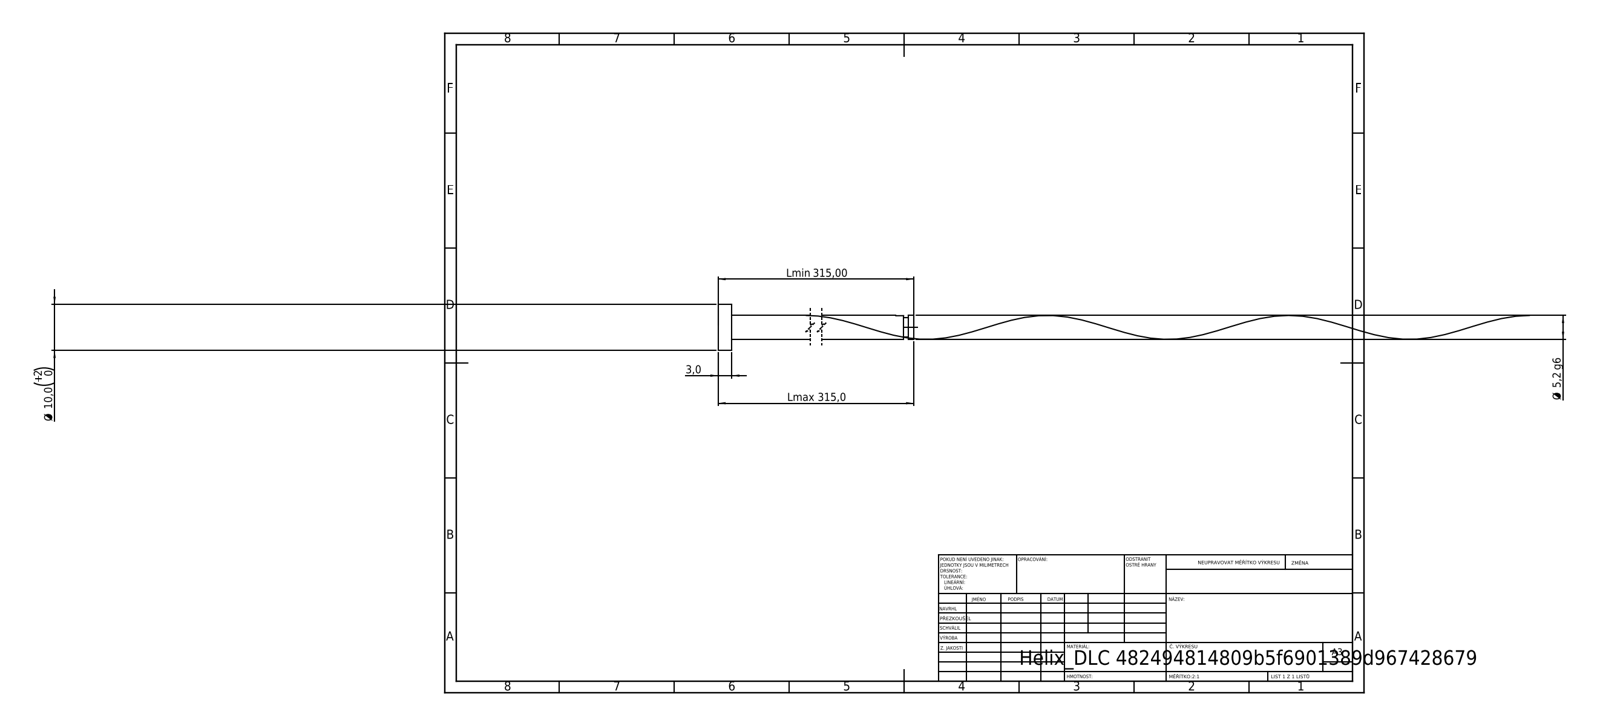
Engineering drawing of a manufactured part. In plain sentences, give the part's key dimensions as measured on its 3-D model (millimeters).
Its 3-D file was written by "SolidWorks 2019 (CONFIG_CONTROL_DESIGN)". It is 1 solid with 16 faces: 6 planar, 9 cylindrical and 1 other. Overall it measures 315 by 10 by 10 millimeters. Its volume is 8 276 cubic millimeters and its surface area 7 157 square millimeters. Round bosses or shafts: 1 of diameter 10, 1 of diameter 5.2, 1 of diameter 4.16. The main face-to-face distances are 3, 315, 312, 313.85, 310.85, 1.15, 312.81, 309.81, 1.04, 2.19.
